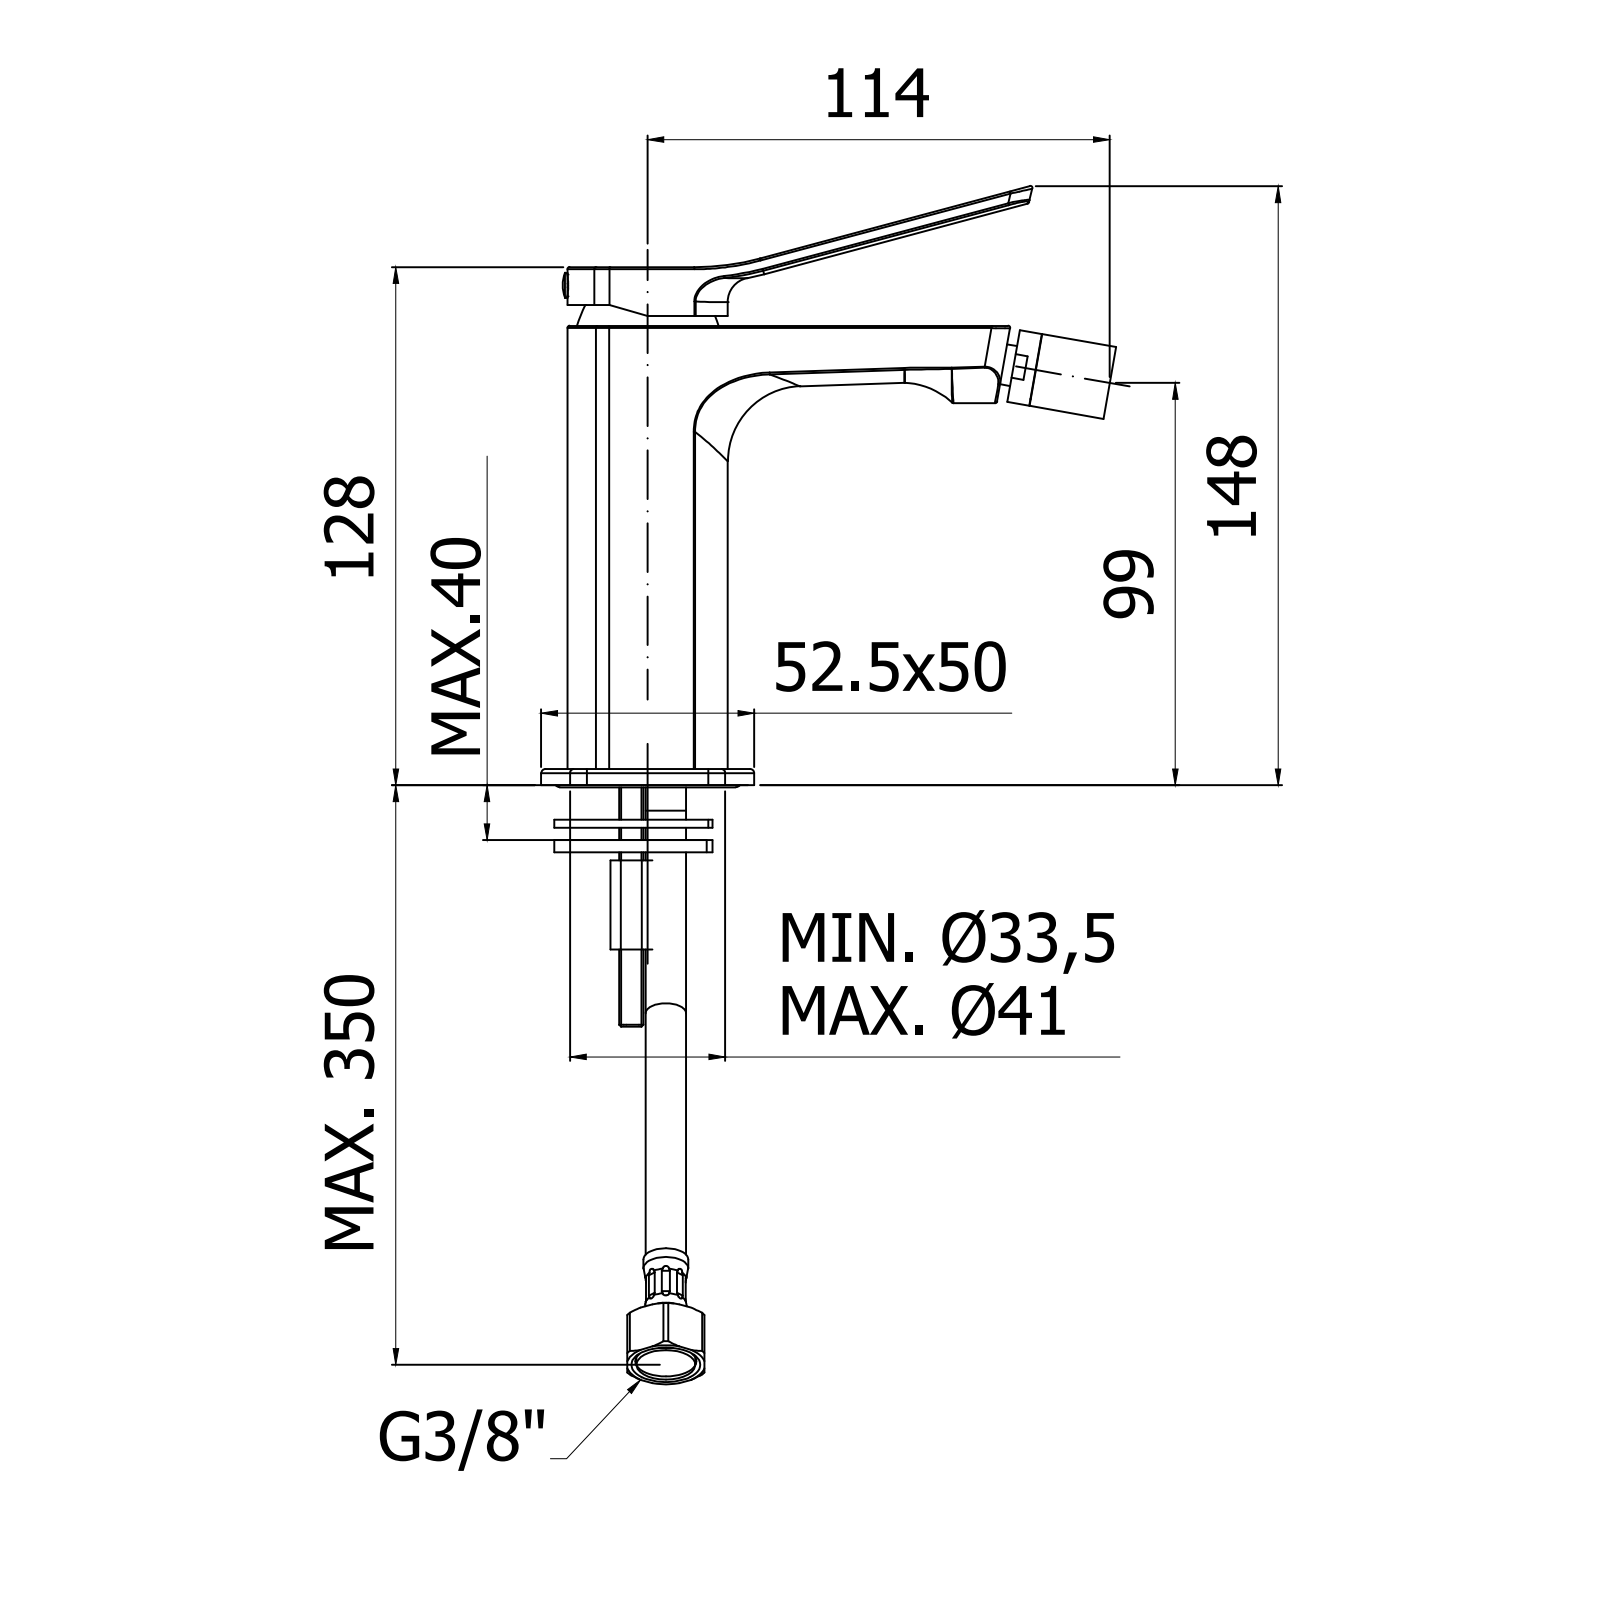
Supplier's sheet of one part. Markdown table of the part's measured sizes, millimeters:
| quantity | value |
| --- | --- |
| part name | TI131CR |
| STEP written by | CREO PARAMETRIC BY PTC INC, 2020044 (CONFIG_CONTROL_DESIGN) |
| units | millimeters |
| bodies | 2 solids, 529 faces (117 planar, 199 cylindrical, 213 other) |
| overall size | 147.66 × 141.75 × 50 |
| volume | 90 415 mm³ |
| surface area | 64 485 mm² |
| round holes (diameter × count) | 4.2 × 2, 5 × 2, 6.2 × 2, 4 × 1, 5.5 × 1, 8 × 1, 10 × 1, 13 × 1, 15 × 1, 26.5 × 1, 28 × 1, 29 × 1 |
| round bosses / shafts (diameter × count) | 41 × 1, 33 × 1, 31.8 × 1, 30.3 × 1, 18 × 1, 14.5 × 1, 10 × 1, 9.5 × 1 |
| partial cylindrical surfaces (radius × count) | 1 × 49, 0.5 × 20, 5 × 14, 4.5 × 4, 22 × 2, 24.5 × 2, 24.87 × 2, 40.09 × 2 |
| main face-to-face distances | 2.5, 110.7, 113.2, 17, 1.5, 4, 13, 122.2, 106.7, 109.2 |
| hole center spacings | 11.7, 13.04, 11, 22 |
